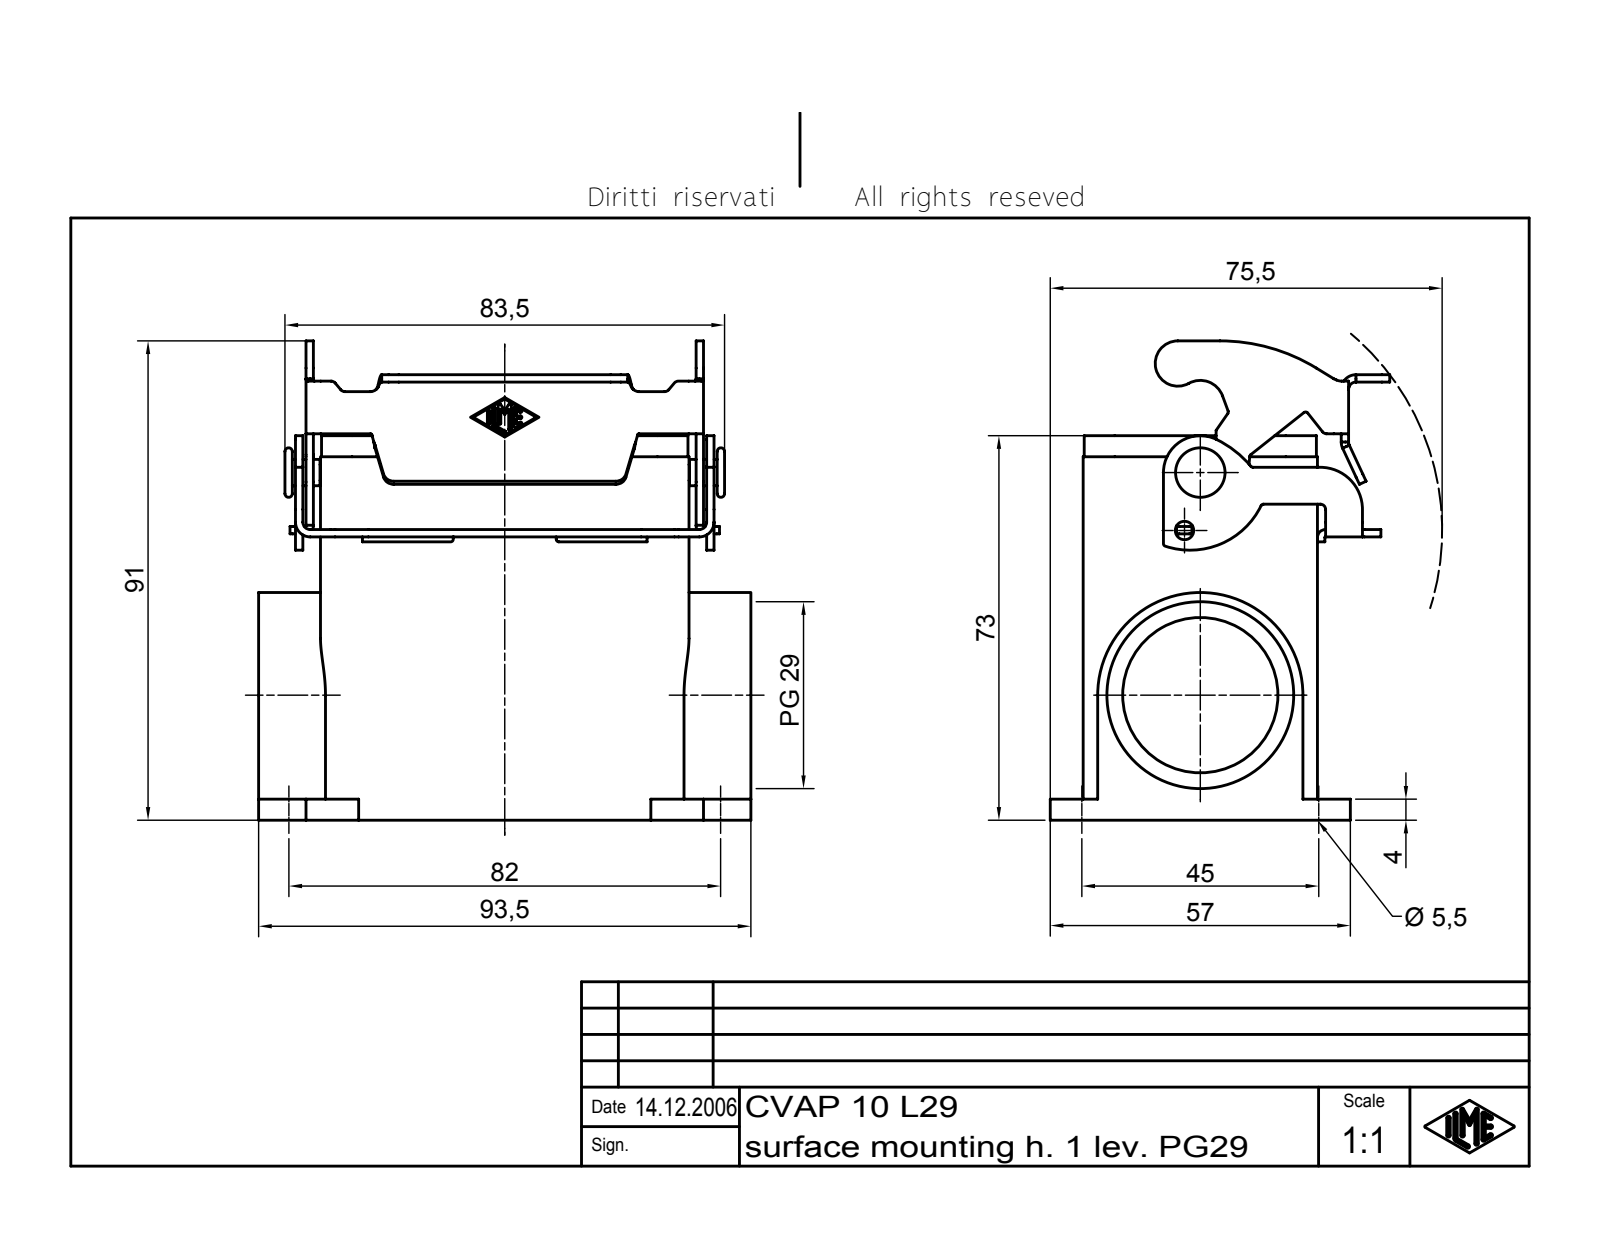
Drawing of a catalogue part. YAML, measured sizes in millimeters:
part_name: "CVAP 10 L29"
step_written_by: "Autodesk Inventor 7 (AUTOMOTIVE_DESIGN)"
units: millimeters
bodies: {solids: 2, faces: 401, planar: 141, cylindrical: 116, other: 144}
overall_size: [93.5, 91, 64.48]
volume: 98036
surface_area: 53272
round_holes:
  - {diameter: 5.5, count: 4}
  - {diameter: 3.5, count: 1}
  - {diameter: 29.48, count: 1}
  - {diameter: 35.48, count: 1}
round_bosses_or_shafts:
  - {diameter: 5, count: 1}
  - {diameter: 3.2, count: 1}
  - {diameter: 3, count: 1}
partial_cylinders:
  - {radius: 0.25, count: 15}
  - {radius: 0.5, count: 9}
  - {radius: 1.5, count: 9}
  - {radius: 1, count: 8}
  - {radius: 1.4, count: 6}
  - {radius: 2, count: 6}
  - {radius: 2.8, count: 6}
  - {radius: 1.8, count: 4}
face_to_face_distances: [4, 40.5, 44.5, 36.5, 10, 1.4, 60, 6, 11.75, 21.75]
hole_center_spacings: [45, 82, 93.54, 31.4]
